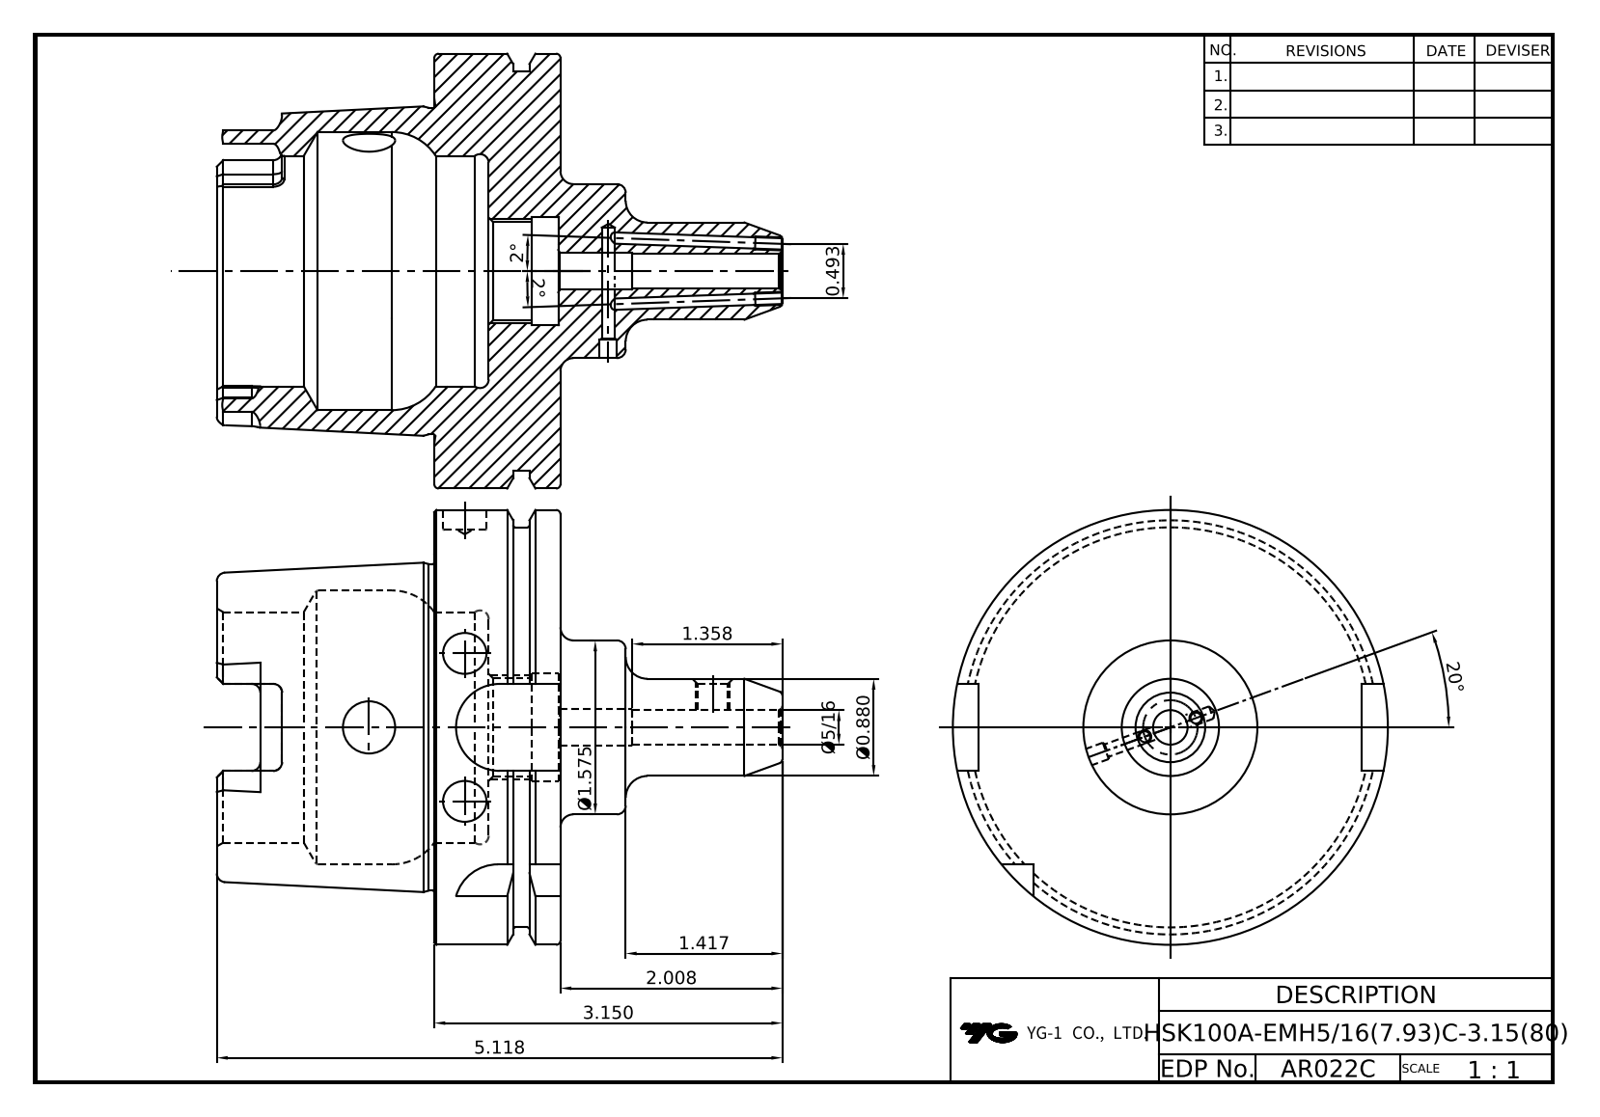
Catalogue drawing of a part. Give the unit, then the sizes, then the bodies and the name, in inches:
Units: inches
Overall size (bounding box): 5.117 × 3.937 × 3.937
Round holes (diameter × count): ⌀0.394 ×3, ⌀0.097 ×2, ⌀0.118 ×1, ⌀0.157 ×1, ⌀0.267 ×1, ⌀0.313 ×1, ⌀0.331 ×1, ⌀0.472 ×1, ⌀0.881 ×1, ⌀0.984 ×1, ⌀2.087 ×1, ⌀2.48 ×1
Round bosses / shafts (diameter × count): ⌀3.937 ×1, ⌀3.622 ×1, ⌀2.969 ×1, ⌀1.575 ×1, ⌀0.88 ×1
Partial cylindrical surfaces — rounded edges, fillets, slot ends (radius × count): R0.079 ×6, R0.192 ×4, R0.394 ×4
Main face-to-face distances: 1.142, 0.492, 0.65, 3.11, 2.461, 1.969, 3.465, 3.091, 1.122, 0.63
Hole centre spacings: 1.299, 2.244
Volume: 17.26 in³ · Surface area: 86.25 in²
Bodies: 1 solid, 133 faces (38 planar, 42 cylindrical, 53 other)
Part name (STEP PRODUCT): LO-HSK100A-EMH7.9375C-80
STEP written by: Autodesk Inventor 2022 (AUTOMOTIVE_DESIGN)
